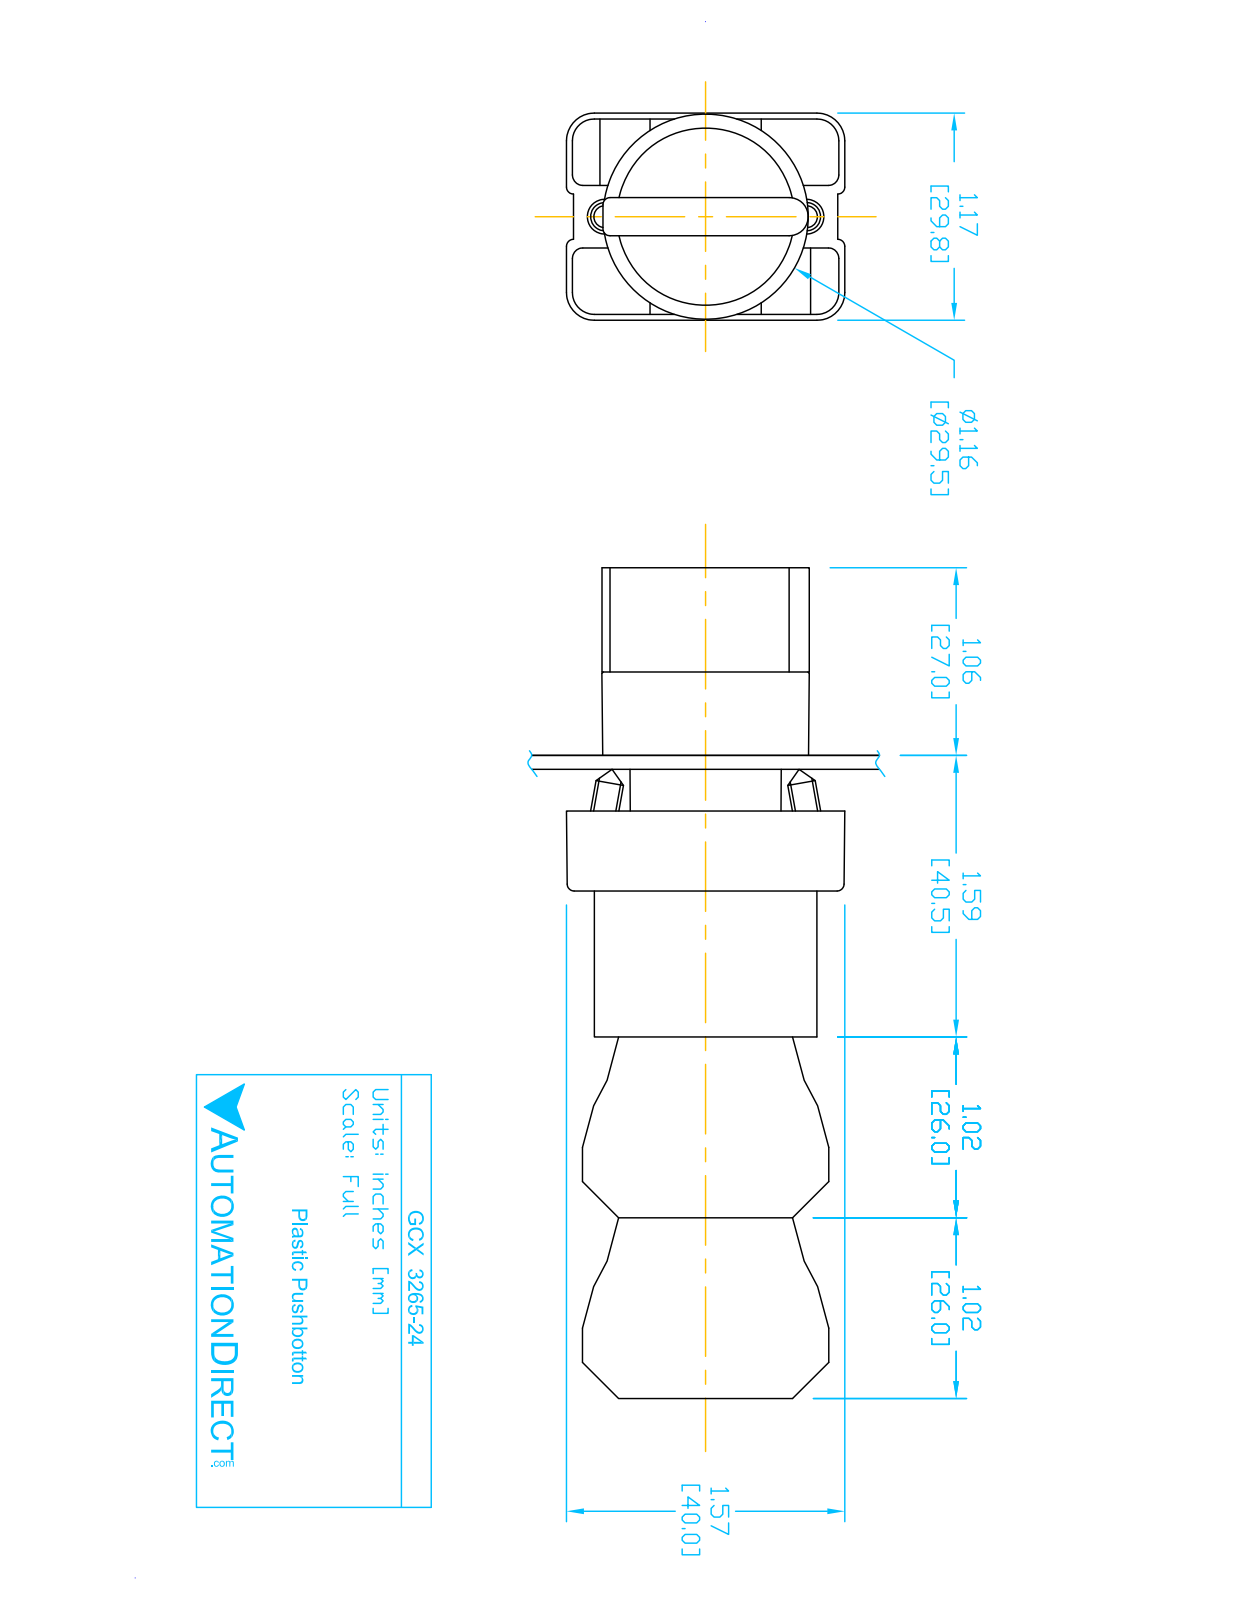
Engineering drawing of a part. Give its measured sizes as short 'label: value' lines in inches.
name: ECX1050; ECX3029-2; ecx1040; GCX3265 OPERATOR (+2 more)
written by: SolidWorks 2016 (AUTOMOTIVE_DESIGN)
unit: in
bodies: 11 solids, 724 faces (488 planar, 193 cylindrical, 43 other)
size: 4.677 × 1.581 × 1.177
volume: 4.751 in³; area: 59.22 in²
holes: 4× ⌀0.079, 2× ⌀0.087, 2× ⌀0.124, 2× ⌀0.13, 1× ⌀0.197, 1× ⌀0.469, 1× ⌀0.878, 1× ⌀0.888, 1× ⌀1.024
bosses: 4× ⌀0.157, 1× ⌀1.175, 1× ⌀1.004, 1× ⌀0.945, 1× ⌀0.856, 1× ⌀0.78, 1× ⌀0.504
rounds: 24× R0.059, 12× R0.041, 12× R0.124, 12× R0.157, 9× R0.039, 2× R0.02, 2× R0.063, 2× R0.079
face distances: 0.579, 0.593, 1.024, 1.171, 0.014, 0.827, 1.85, 3.043, 2.02, 1.193
hole spacings: 0.236, 1.003, 0.974, 0.472, 0.539, 0.544, 1.083, 0.484
